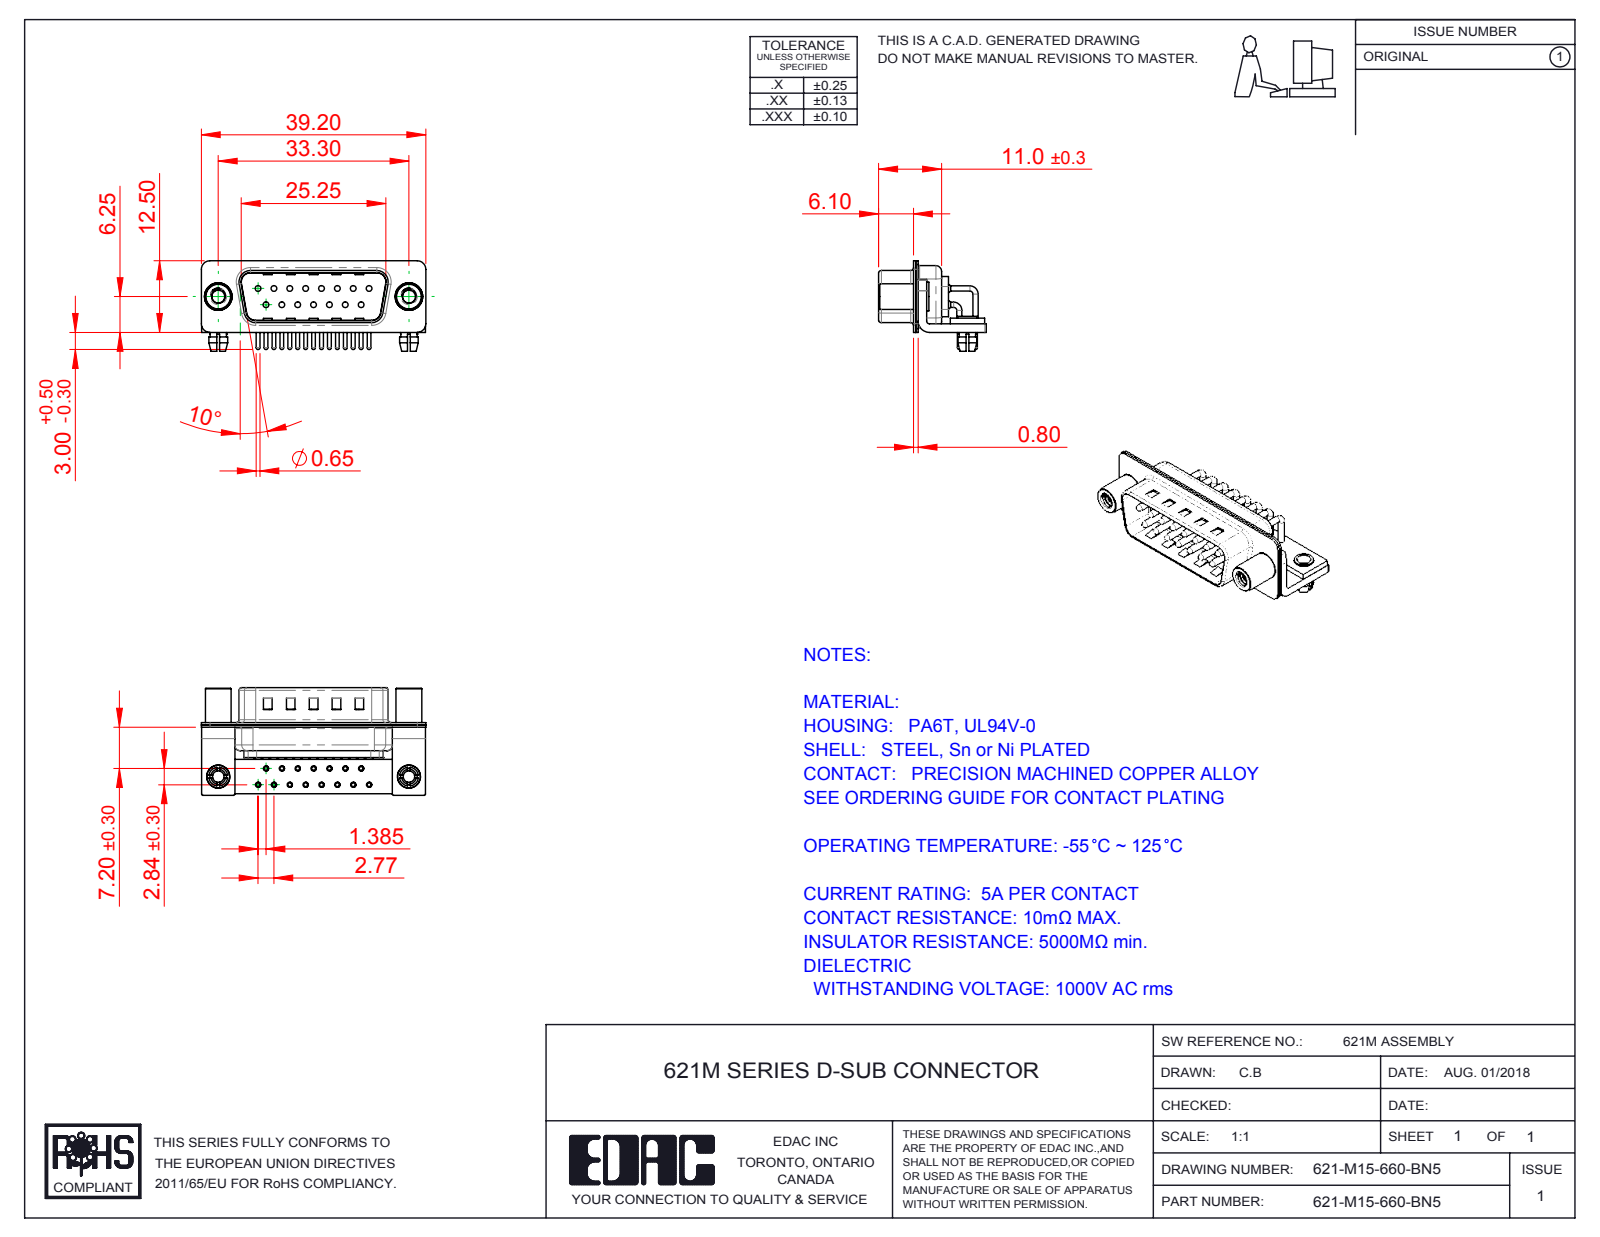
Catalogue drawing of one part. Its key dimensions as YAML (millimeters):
part_name: "621M Housing_15 Contacts; 621M Contact Row 2; 621M Stabilizer Bracket; 621M Shell Front_15 Contacts (+6 more)"
step_written_by: "SolidWorks 2016 (CONFIG_CONTROL_DESIGN)"
units: millimeters
bodies: {solids: 25, faces: 2212, planar: 1175, cylindrical: 799, other: 238}
overall_size: [39.2, 18.8, 15.8]
volume: 2544
surface_area: 6913
round_holes:
  - {diameter: 2, count: 17}
  - {diameter: 0.9, count: 15}
  - {diameter: 1, count: 15}
  - {diameter: 1.7, count: 15}
  - {diameter: 2.26, count: 2}
  - {diameter: 2.5, count: 2}
  - {diameter: 3.2, count: 2}
  - {diameter: 4, count: 2}
  - {diameter: 4.8, count: 2}
round_bosses_or_shafts:
  - {diameter: 0.9, count: 22}
  - {diameter: 1.5, count: 15}
  - {diameter: 0.65, count: 15}
  - {diameter: 5, count: 2}
  - {diameter: 4.9, count: 2}
  - {diameter: 4.5, count: 2}
  - {diameter: 4, count: 2}
  - {diameter: 3.4, count: 2}
partial_cylinders:
  - {radius: 0.25, count: 16}
  - {radius: 1.5, count: 16}
  - {radius: 1.01, count: 15}
  - {radius: 2, count: 13}
  - {radius: 0.5, count: 9}
  - {radius: 1.6, count: 8}
  - {radius: 0.6, count: 4}
  - {radius: 0.65, count: 4}
face_to_face_distances: [0.4, 0.85, 1.5, 0.8, 1.25, 10.4, 9.55, 1, 1.9, 8.3]
hole_center_spacings: [3.16, 2.77, 5.54, 8.31, 11.08, 5.03, 5.04, 7.48]
